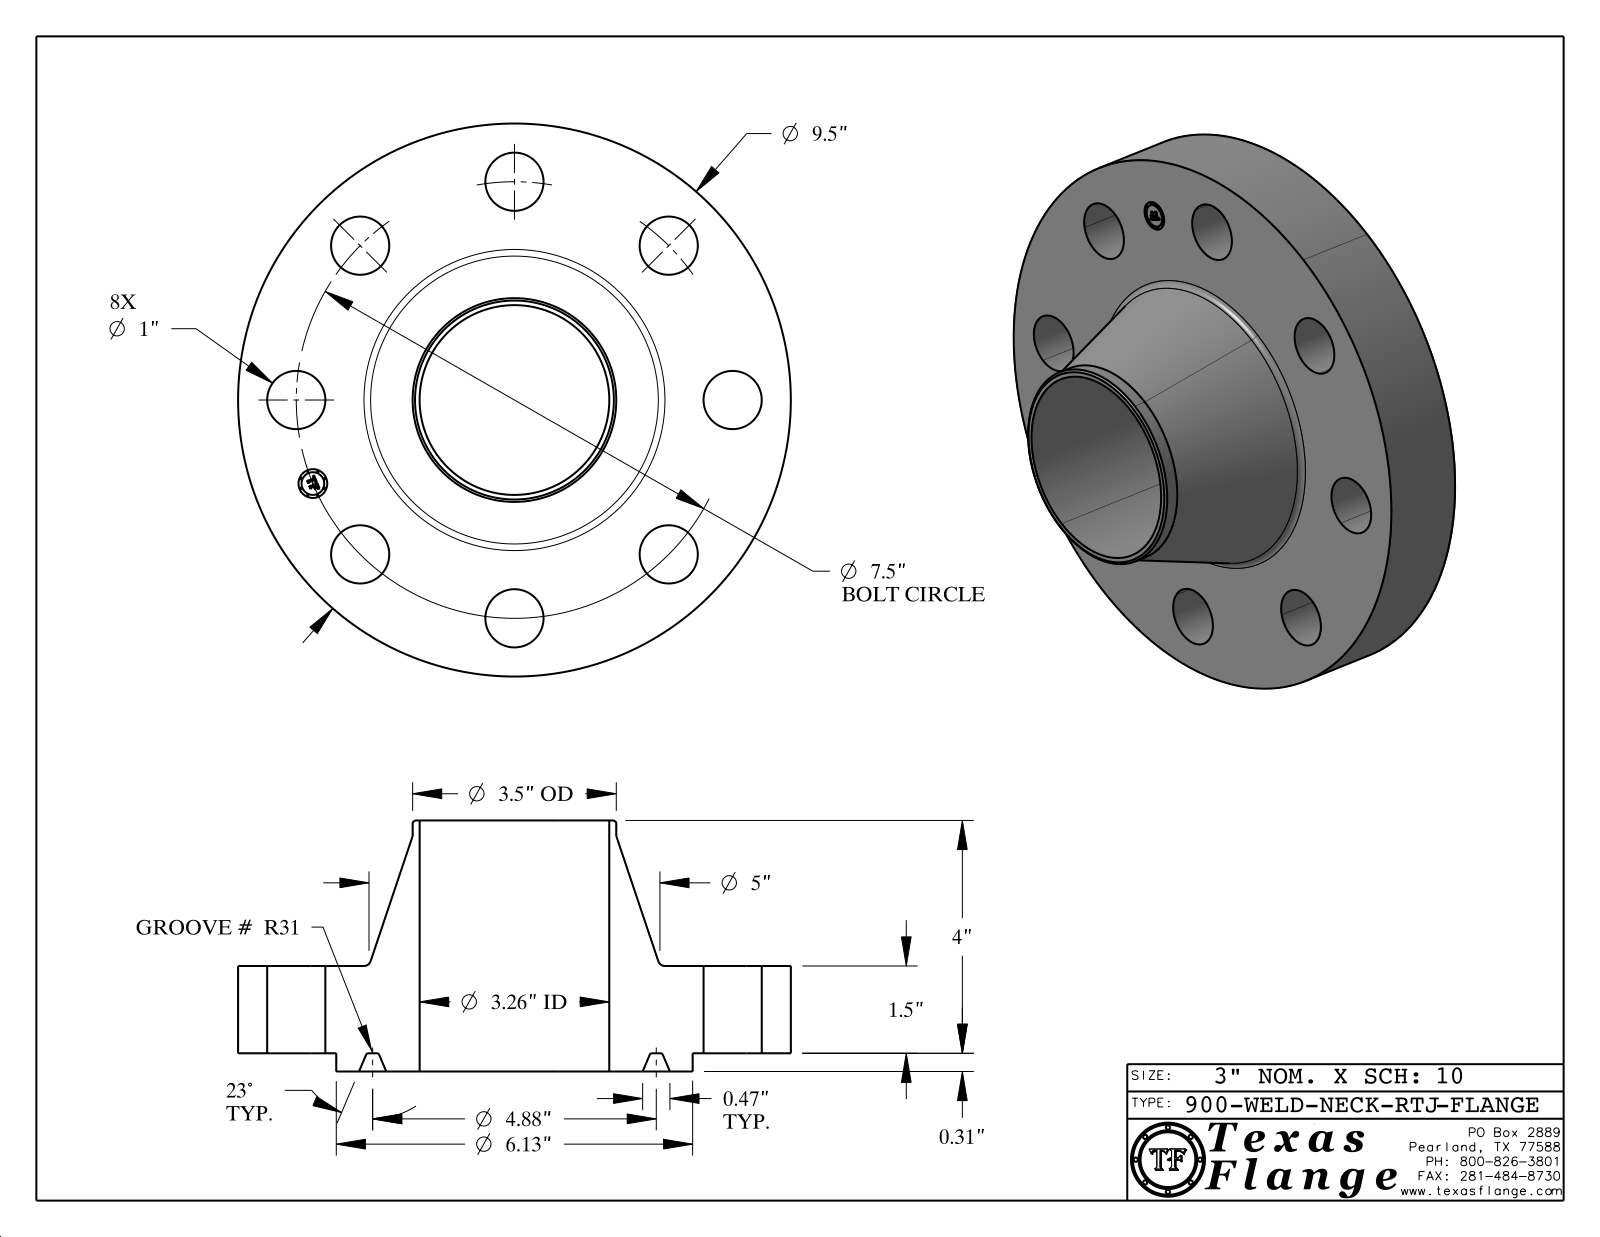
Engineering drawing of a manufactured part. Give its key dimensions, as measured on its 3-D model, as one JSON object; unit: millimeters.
{"part_name": "900-WELD-NECK-RTJ", "step_written_by": "CATIA V5 STEP AP214 (AUTOMOTIVE_DESIGN)", "units": "millimeters", "bodies": {"solids": 1, "faces": 429, "planar": 371, "cylindrical": 44, "other": 14}, "overall_size": [241.3, 241.3, 109.6], "volume_mm3": 1690000, "surface_area_mm2": 177500, "round_holes": [[25.4, 8], [12.6, 1], [82.8, 1]], "round_bosses_or_shafts": [[0.8, 8], [241.3, 1], [155.6, 1], [88.9, 1], [9.9, 1]], "face_to_face_distances": [38.1, 8, 46.1, 109.6, 101.6, 63.5, 0.4, 45.7, 37.7, 63.9], "hole_center_spacings": [95.3, 72.9, 134.7, 176, 37.2, 158.4, 186.8, 190.5]}
